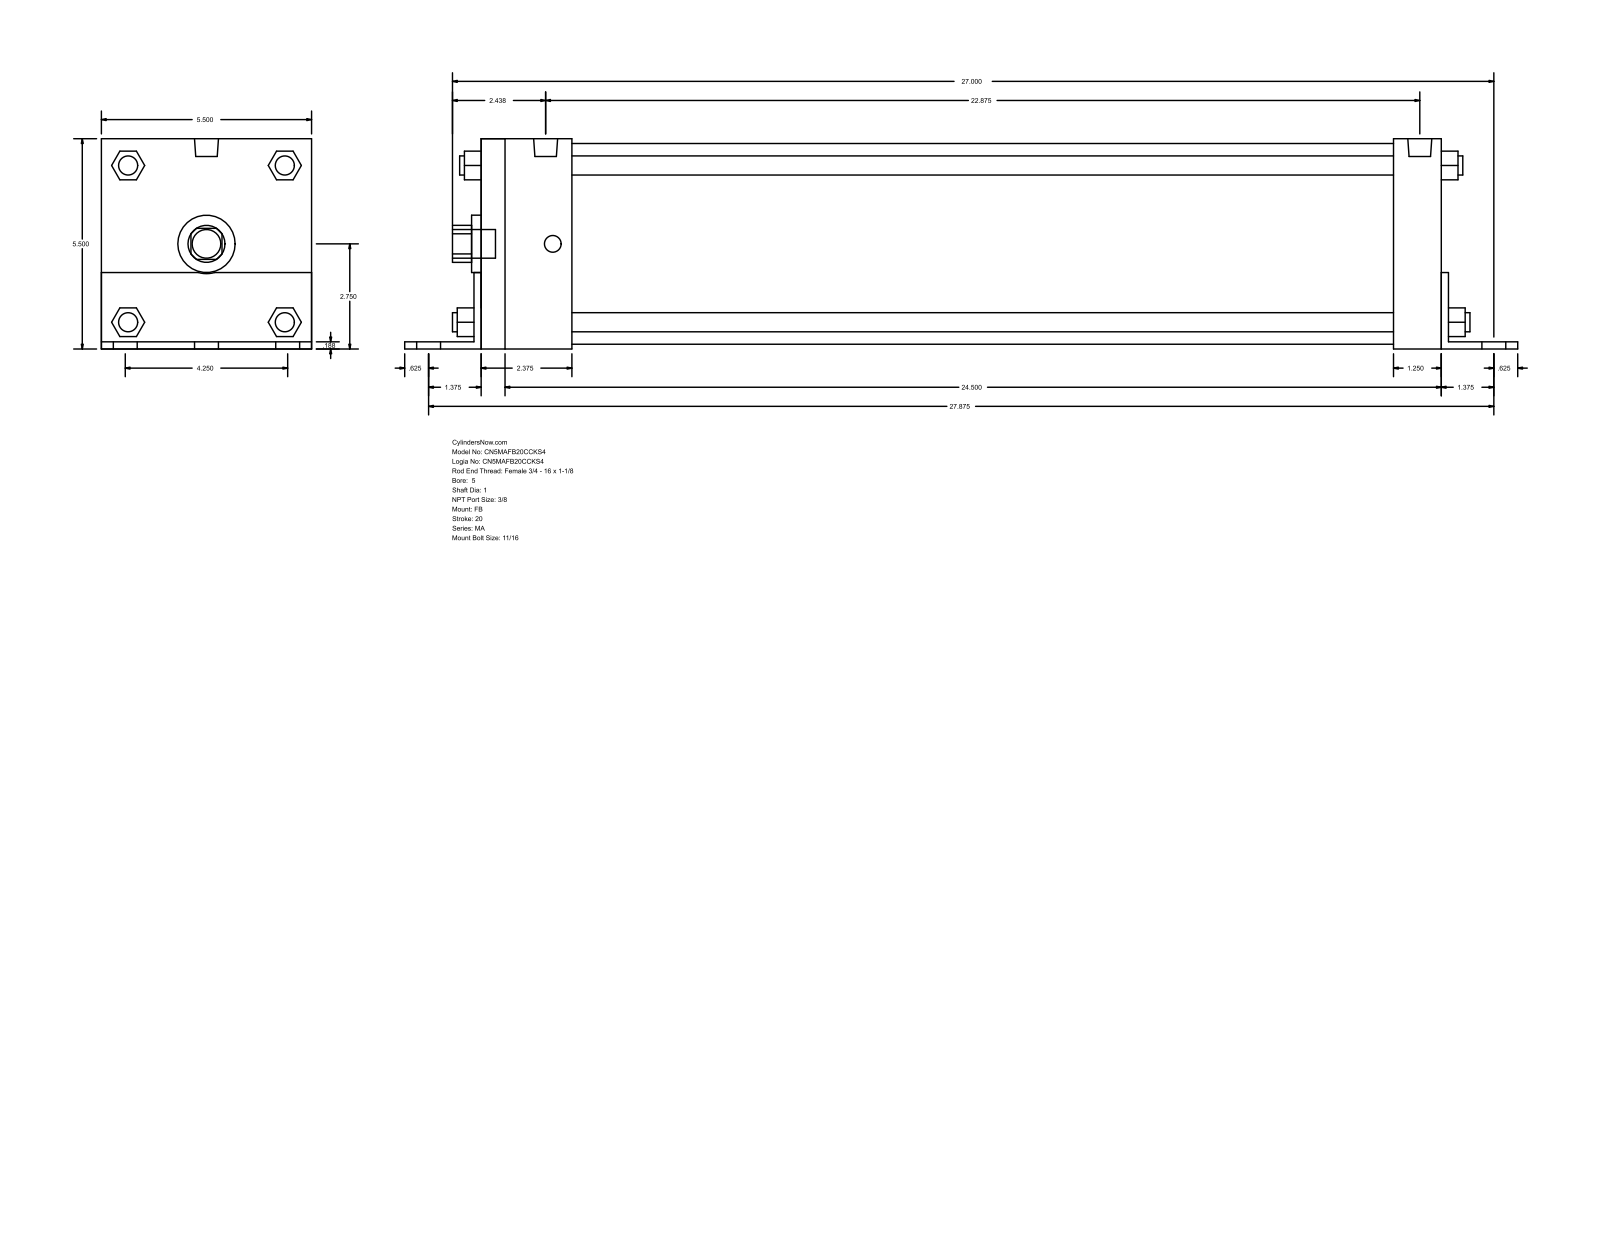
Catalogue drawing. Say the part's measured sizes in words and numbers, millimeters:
The part is named "MA_FB__0500_1". Its 3-D file was written by "GSSL Pune (CONFIG_CONTROL_DESIGN)". It is 0 solids with 140 faces: 105 planar, 35 cylindrical and 0 other. Overall it measures 739.77 by 139.75 by 139.7 millimeters. Round holes: 1 of diameter 25.4, 1 of diameter 38.1, 1 of diameter 133.35. Round bosses or shafts: 6 of diameter 17.46, 4 of diameter 12.7, 4 of diameter 11.11, 2 of diameter 15.93, 1 of diameter 19.05. Partial cylindrical surfaces (rounded edges, fillets, slot ends): 1 of radius 12.29, 1 of radius 19.81. The main face-to-face distances are 139.7, 4.76, 139.75, 642.94, 4.71, 134.99, 638.18, 647.7, 31.75, 36.51.
